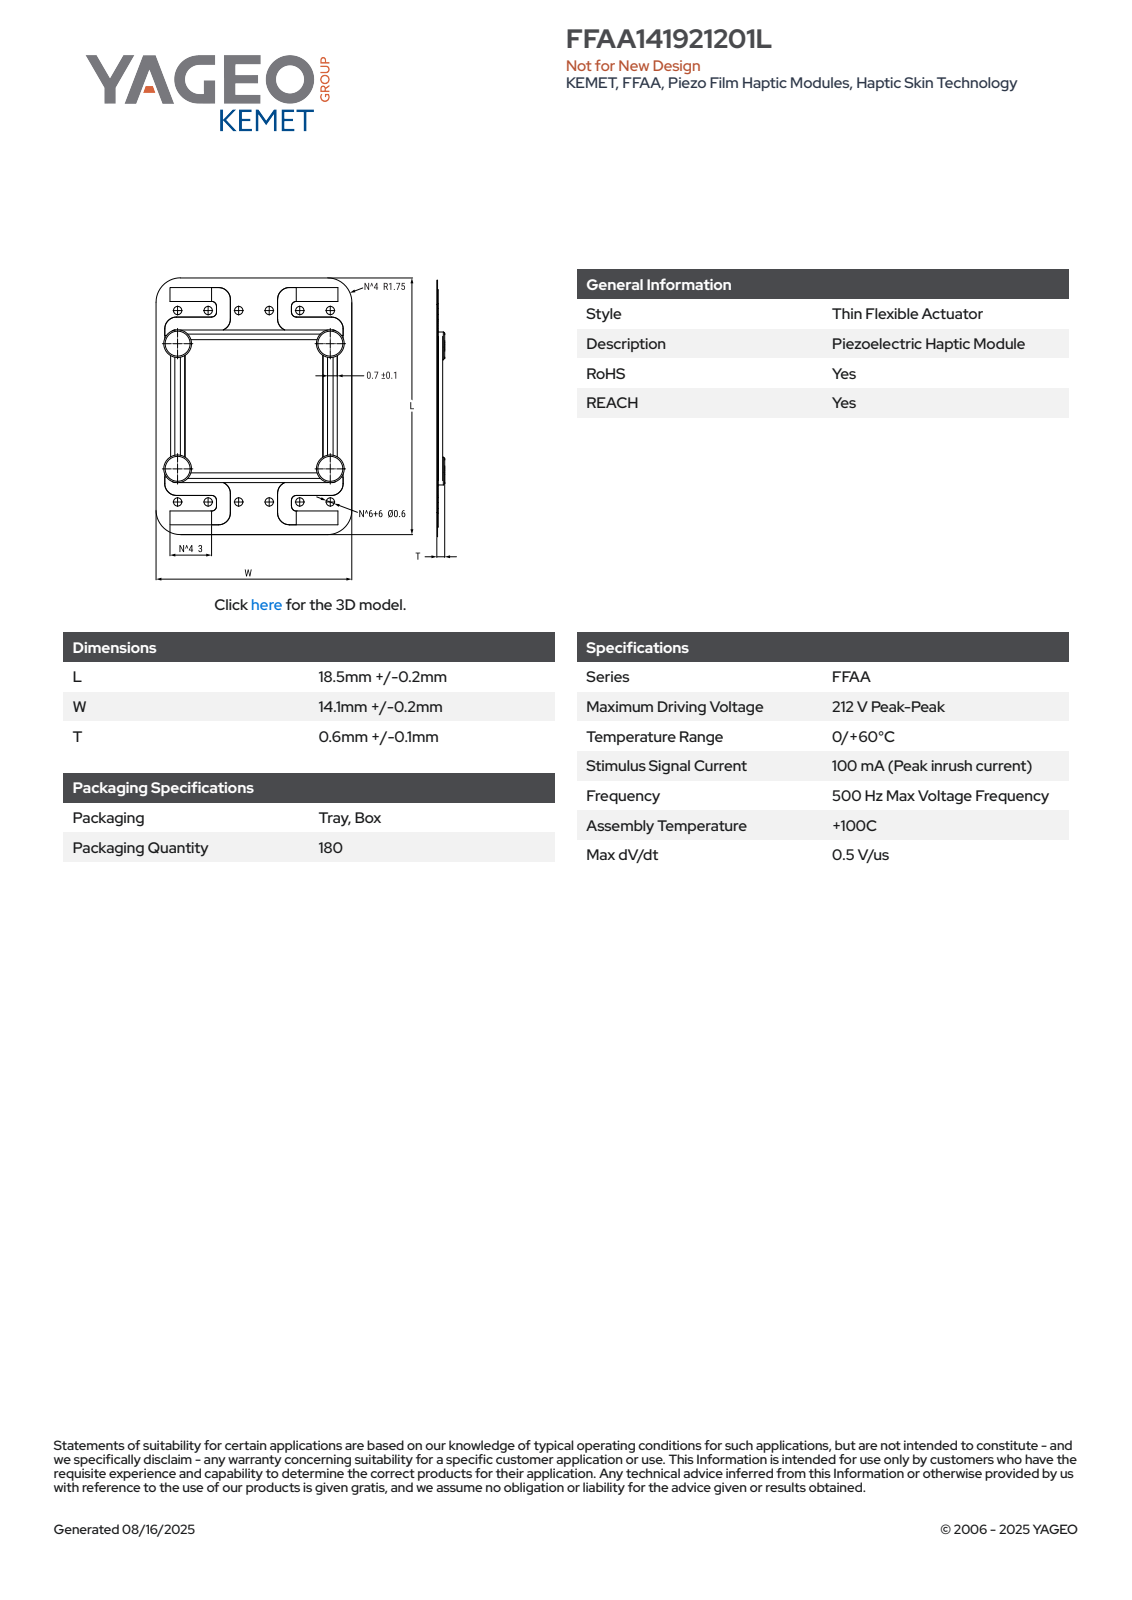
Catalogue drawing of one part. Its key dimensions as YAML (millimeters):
part_name: "200-00006_REV02_OP4_SINGLE-6524.stp; 200-00006_REV02_OP4_SINGL-38336.stp; WIP00009418_00__ASM.stp; 200-00006_REV02_OP4_SINGL-15815.stp (+4 more)"
step_written_by: "SolidWorks 2021 (AUTOMOTIVE_DESIGN)"
units: millimeters
bodies: {solids: 5, faces: 214, planar: 90, cylindrical: 78, other: 46}
overall_size: [18.5, 14.1, 0.6]
volume: 14
surface_area: 945
round_bosses_or_shafts:
  - {diameter: 1, count: 2}
partial_cylinders:
  - {radius: 0.25, count: 24}
  - {radius: 0.85, count: 12}
  - {radius: 0.35, count: 8}
  - {radius: 0.75, count: 6}
  - {radius: 0.3, count: 4}
  - {radius: 1.75, count: 4}
face_to_face_distances: [0.42, 0.53, 0.54, 0.59, 14.1, 18.5, 0.63, 1, 13.47, 0.4]
